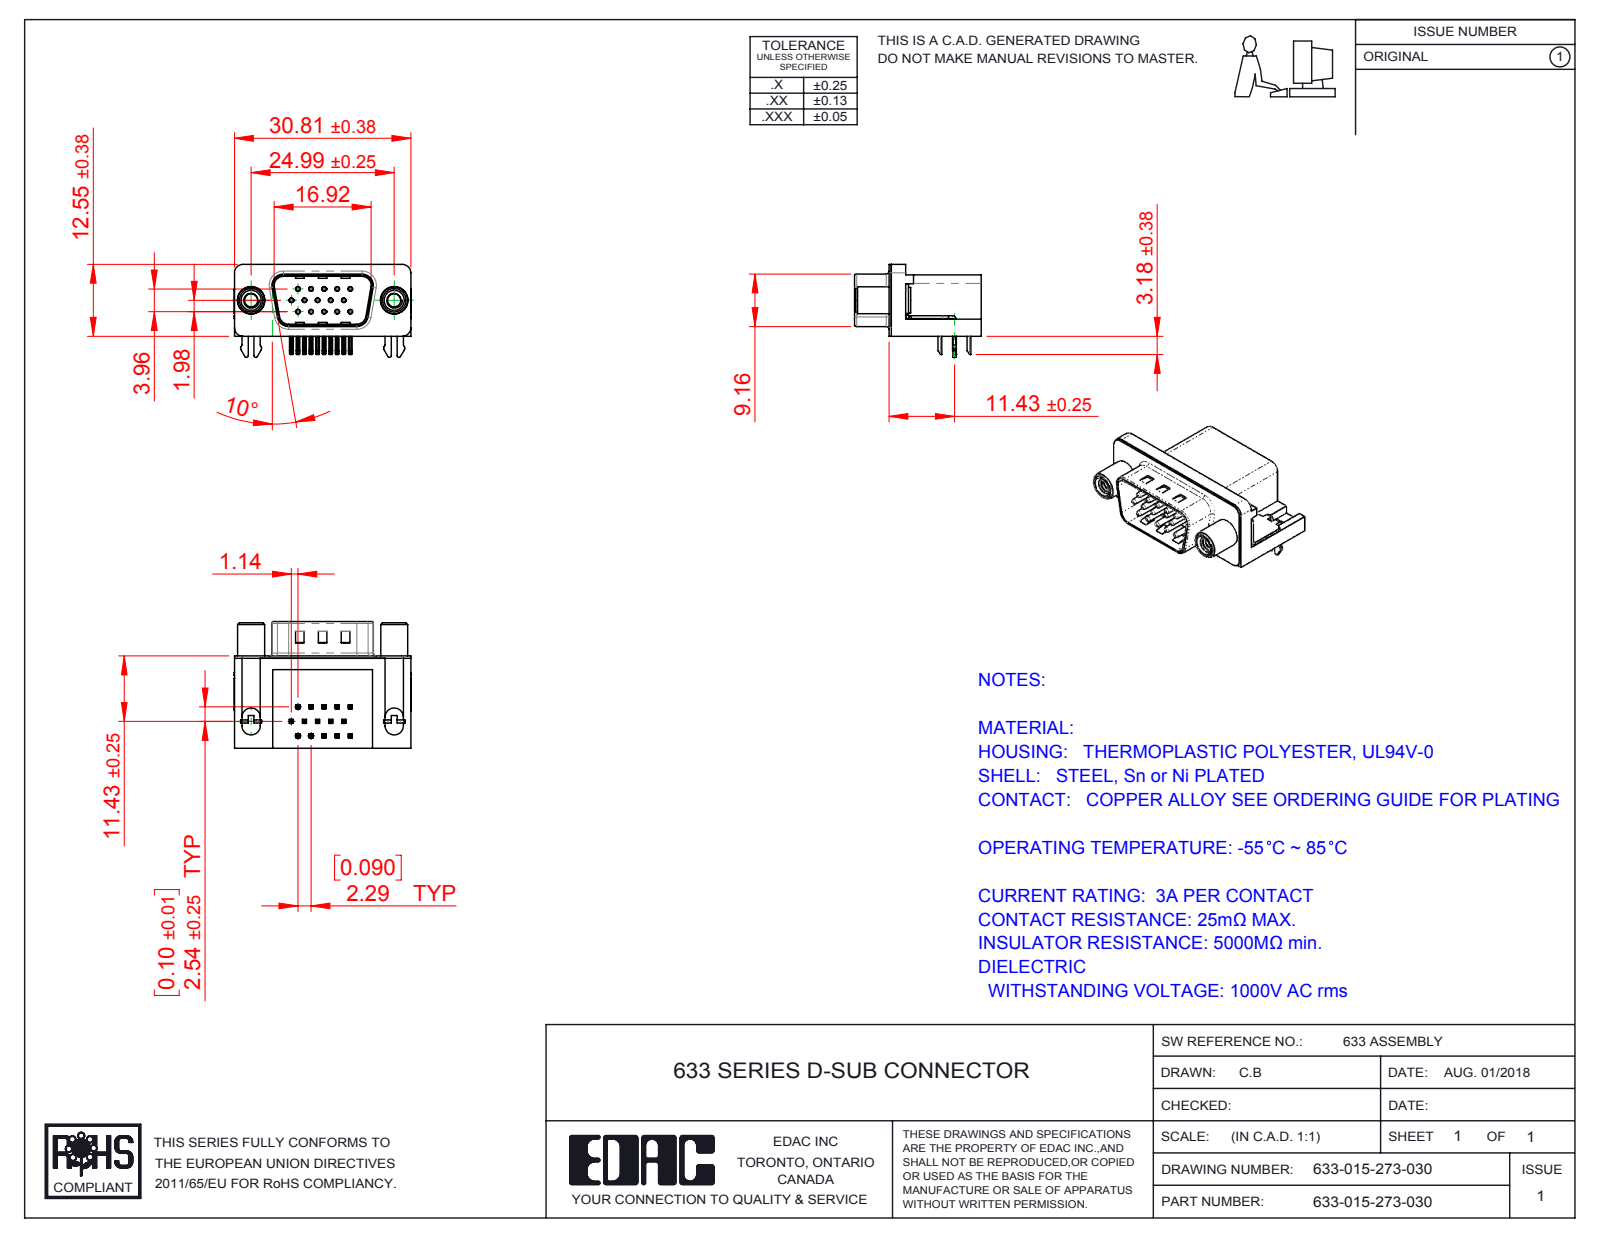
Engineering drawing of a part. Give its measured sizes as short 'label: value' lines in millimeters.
name: 633 Contact Middle_Recessed; 633-015-273-030; 633 Contact Bottom; 633 Round Threaded Standoff (+5 more)
written by: SolidWorks 2016 (CONFIG_CONTROL_DESIGN)
unit: mm
bodies: 21 solids, 1477 faces (885 planar, 459 cylindrical, 133 other)
size: 30.89 × 22.1 × 16.25
volume: 4 163 mm³; area: 5 625 mm²
holes: 15× ⌀0.35, 15× ⌀0.8, 2× ⌀2.3, 2× ⌀3.1, 2× ⌀4, 2× ⌀4.8, 2× ⌀5
bosses: 15× ⌀0.75, 2× ⌀4.9, 2× ⌀4.7, 2× ⌀4.5, 2× ⌀3.85
rounds: 60× R0.25, 30× R0.12, 16× R1, 14× R0.5, 8× R1.6, 7× R1.5, 4× R0.32, 4× R0.9
face distances: 0.4, 10.35, 15.7, 2.9, 6.7, 2.5, 16.1, 0.5, 0.35, 10.7
hole spacings: 3.96, 2.28, 4.57, 2.29, 6.05, 6.86, 7.92, 6.04
